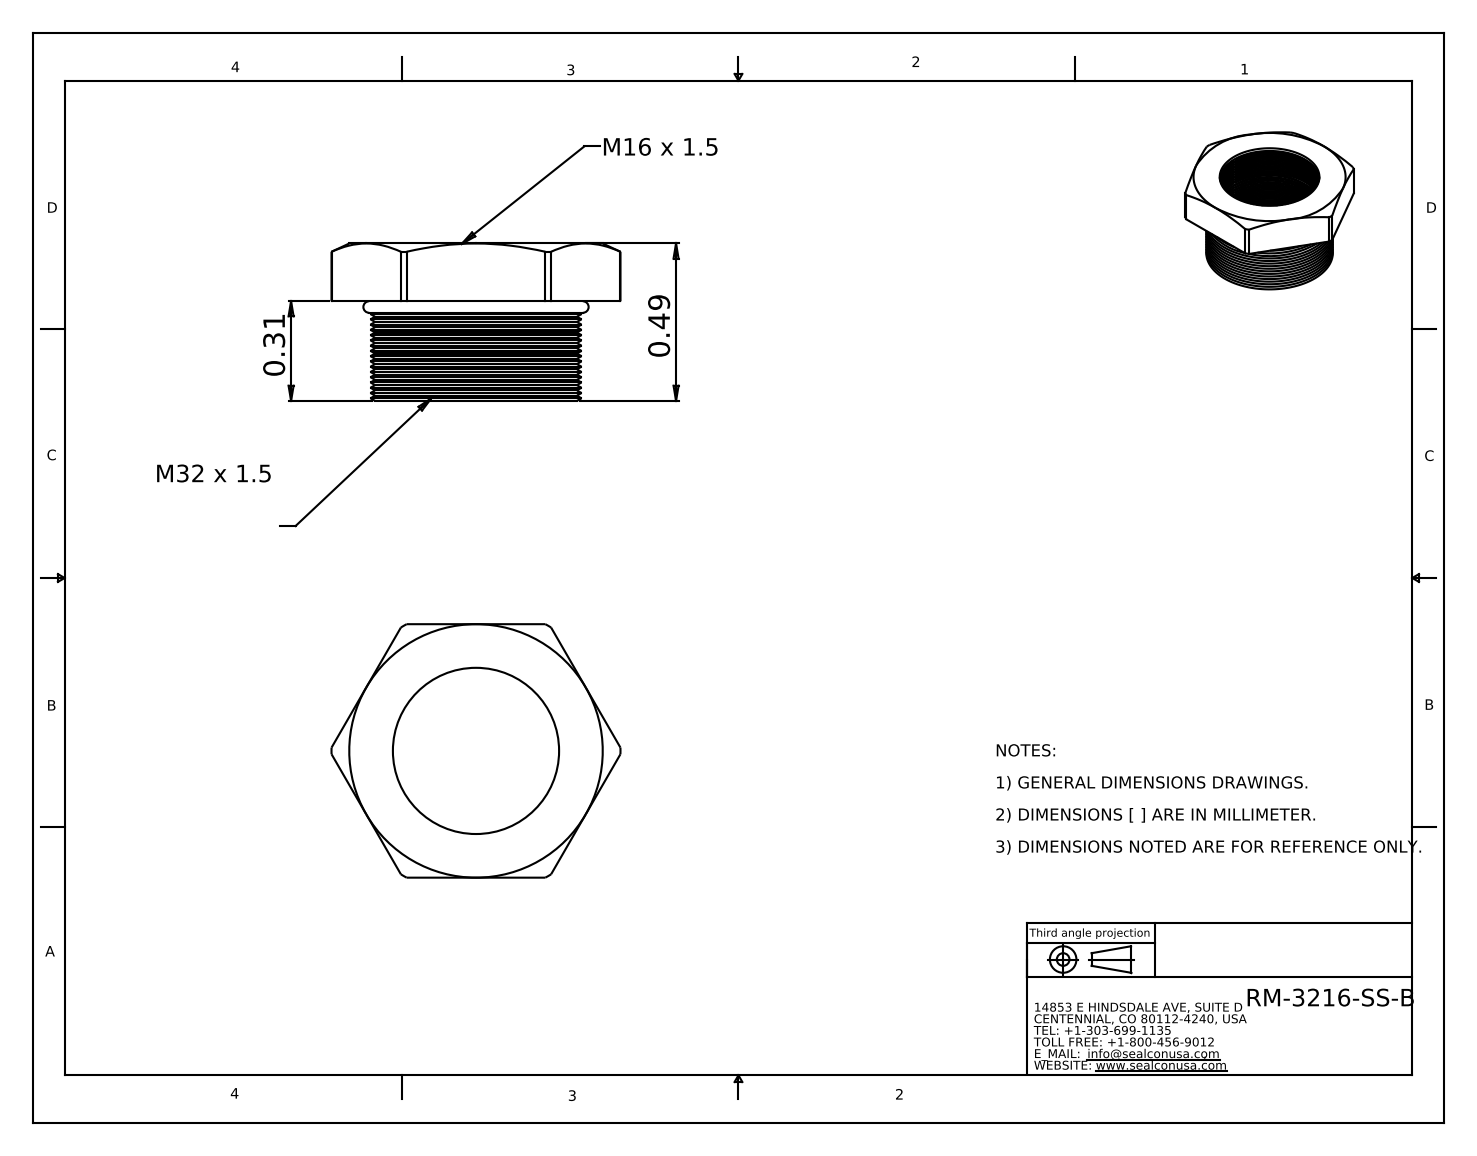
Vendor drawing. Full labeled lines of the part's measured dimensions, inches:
Part name (STEP PRODUCT): RM-3216-SS-B
STEP written by: SolidWorks 2008 (CONFIG_CONTROL_DESIGN)
Units: inches
Bodies: 2 solids, 313 faces (9 planar, 105 cylindrical, 199 other)
Overall size (bounding box): 0.901 × 0.79 × 0.49
Volume: 0.094 in³ · Surface area: 4.155 in²
Round holes (diameter × count): ⌀0.518 ×1
Round bosses / shafts (diameter × count): ⌀0.63 ×1
Partial cylindrical surfaces — rounded edges, fillets, slot ends (radius × count): R0.45 ×1
Main face-to-face distances: 0.18, 0.79, 0.31, 0.49
